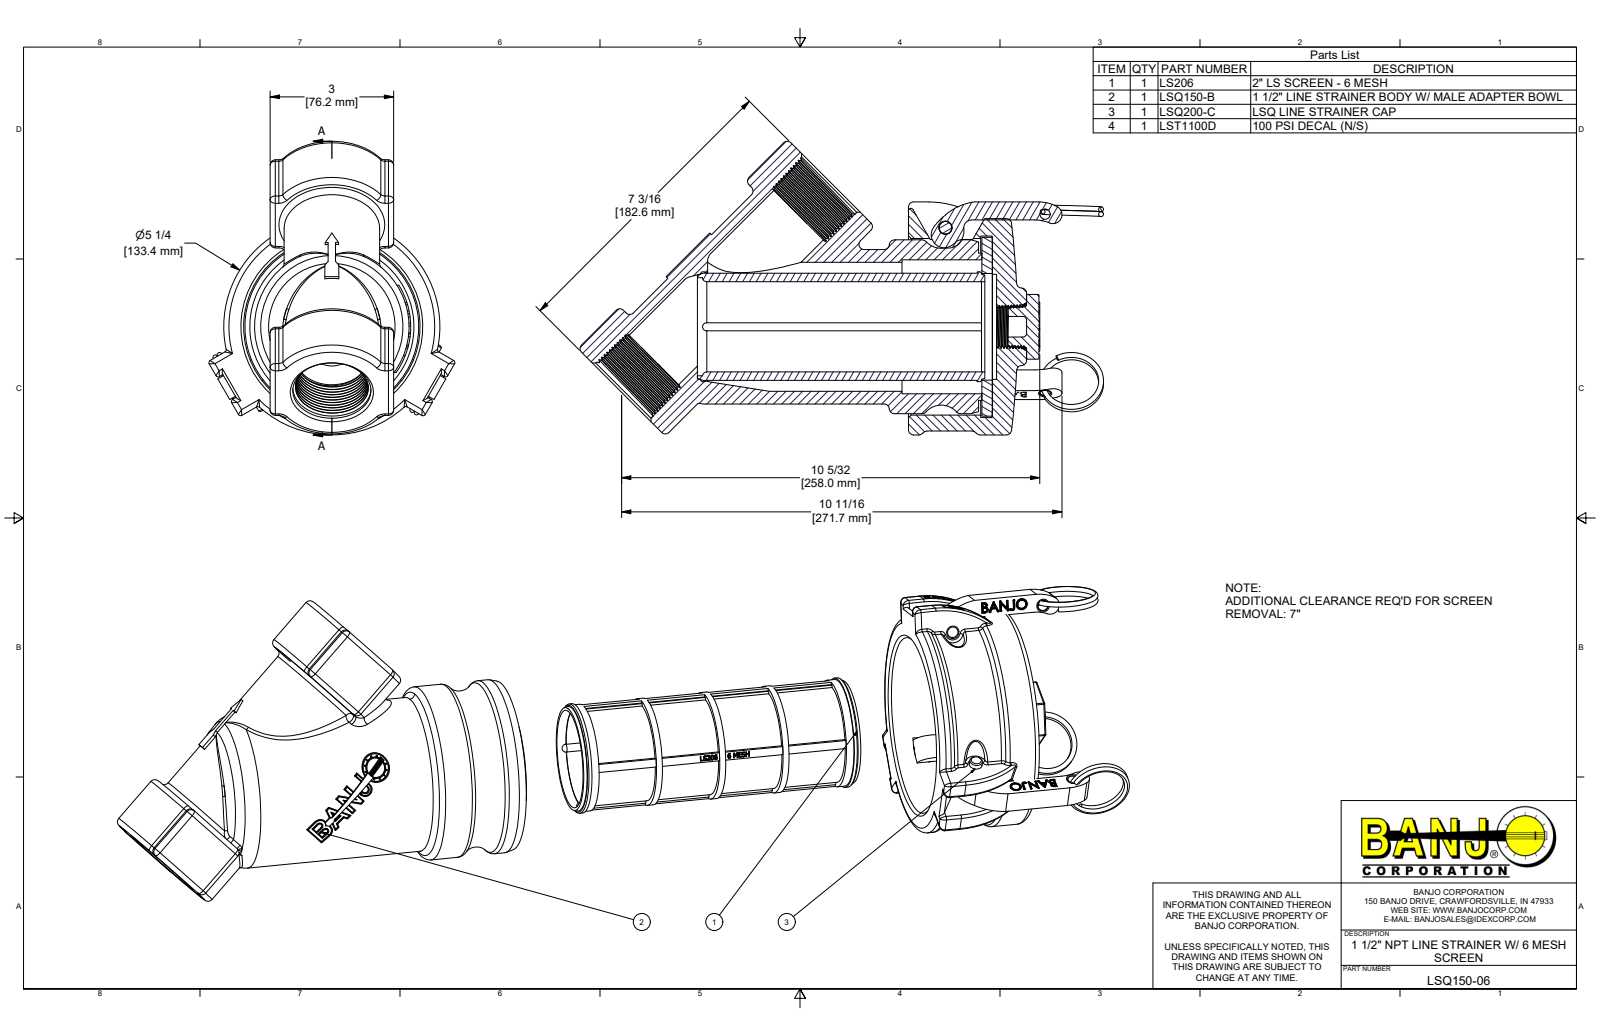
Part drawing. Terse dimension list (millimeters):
name: LSQ150-06; LSQ150-B; LSQ200-C; LSQ200-MYC (+8 more)
written by: Autodesk Inventor 2019 (AUTOMOTIVE_DESIGN)
unit: mm
bodies: 15 solids, 3438 faces (1180 planar, 828 cylindrical, 1430 other)
size: 484.2 × 181 × 151.7
volume: 1 293 000 mm³; area: 406 800 mm²
holes: 3× ⌀6.4, 3× ⌀7.9, 3× ⌀8.1, 2× ⌀43.2, 1× ⌀11.5, 1× ⌀12.7, 1× ⌀16.3, 1× ⌀55.6, 1× ⌀59.7, 1× ⌀64.8, 1× ⌀65.8, 1× ⌀79.5
bosses: 3× ⌀8.3, 3× ⌀7.9, 1× ⌀133.4, 1× ⌀110.2, 1× ⌀107.2, 1× ⌀95.3, 1× ⌀90.7, 1× ⌀67.7
rounds: 353× R0.2, 51× R0.1, 47× R3.2, 27× R1.5, 18× R0.8, 6× R23.6, 5× R6.4, 4× R2.5
face distances: 6.4, 6.5, 51.8, 51.7, 45.3, 11.4, 15.5, 2.5, 9, 0.8
hole spacings: 62, 85.3, 144.4
